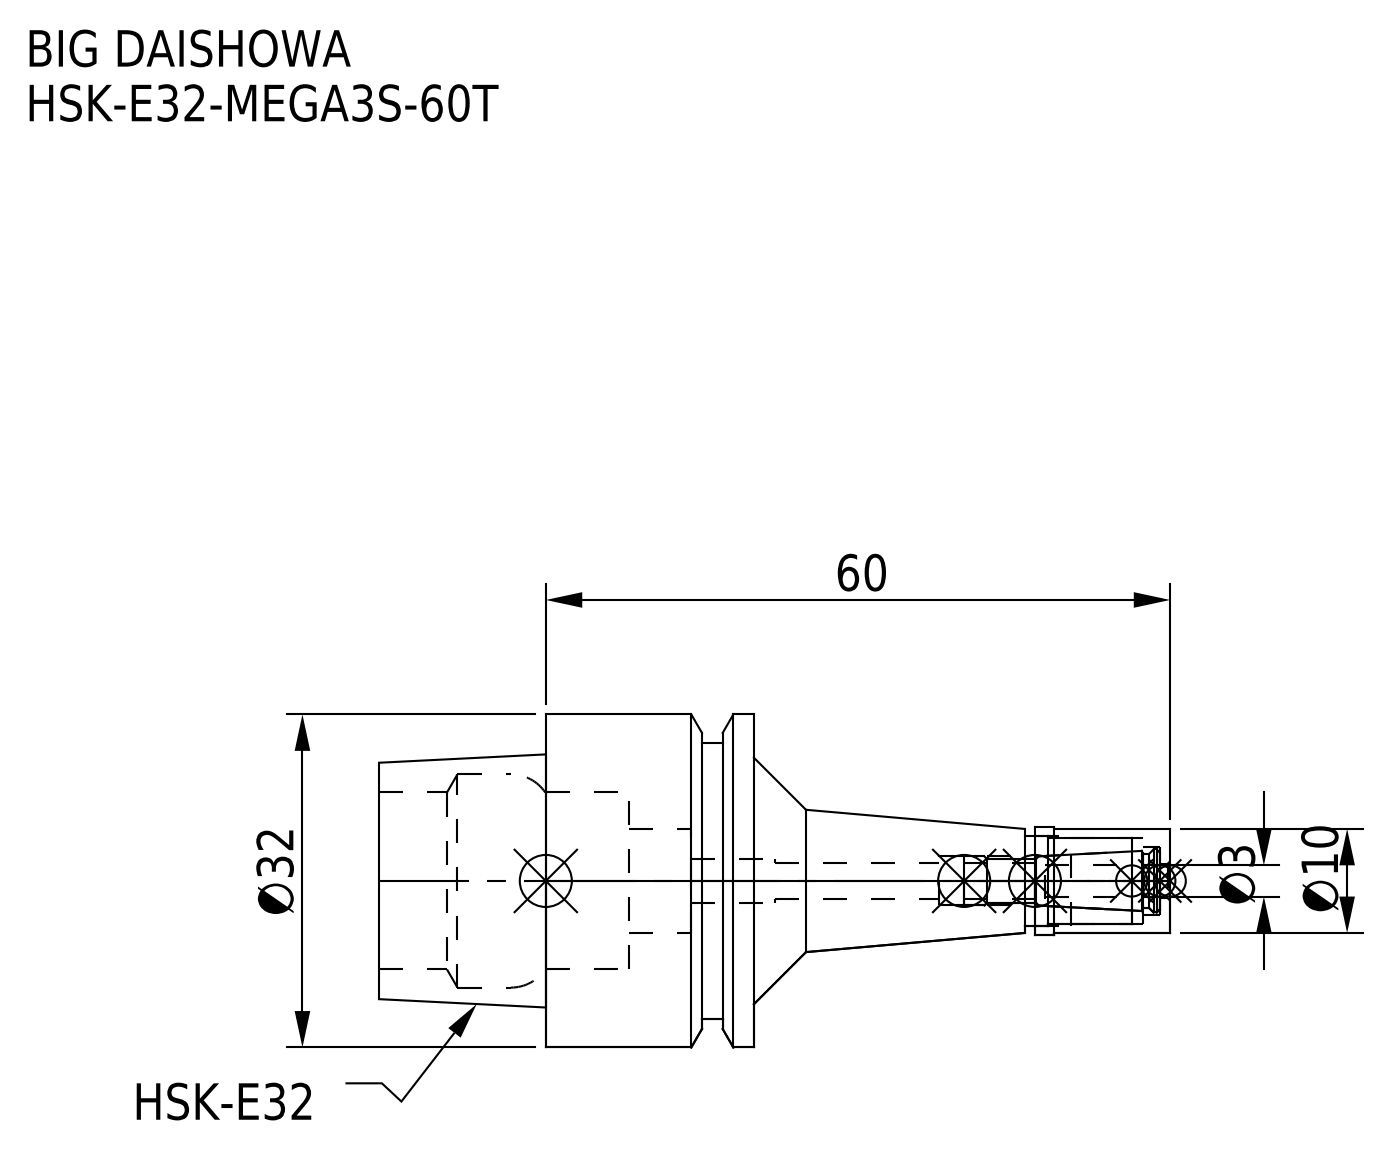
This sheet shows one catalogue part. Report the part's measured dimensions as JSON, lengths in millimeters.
{"part_name": "HSK-E32-MEGA3S-60T-030.stp; HSK-E32-MEGA3S-60T; HSK-E32-MEGA3S-60T-030-FreeParts; MGN3S_1.stp (+3 more)", "step_written_by": "SolidWorks 2019 (CONFIG_CONTROL_DESIGN)", "units": "millimeters", "bodies": {"solids": 2, "faces": 74, "planar": 18, "cylindrical": 38, "other": 18}, "overall_size": [76, 32, 32], "volume_mm3": 19710, "surface_area_mm2": 9227, "round_holes": [[3.3, 1], [3.4, 1], [4.2, 1], [4.7, 1], [6.6, 1], [8.2, 1], [8.7, 1], [10, 1], [17, 1], [20.5, 1]], "round_bosses_or_shafts": [[32, 1], [26.5, 1], [10.3, 1]], "face_to_face_distances": [20, 36, 16, 12.05, 7.95, 23.95, 31, 2, 5, 3]}
